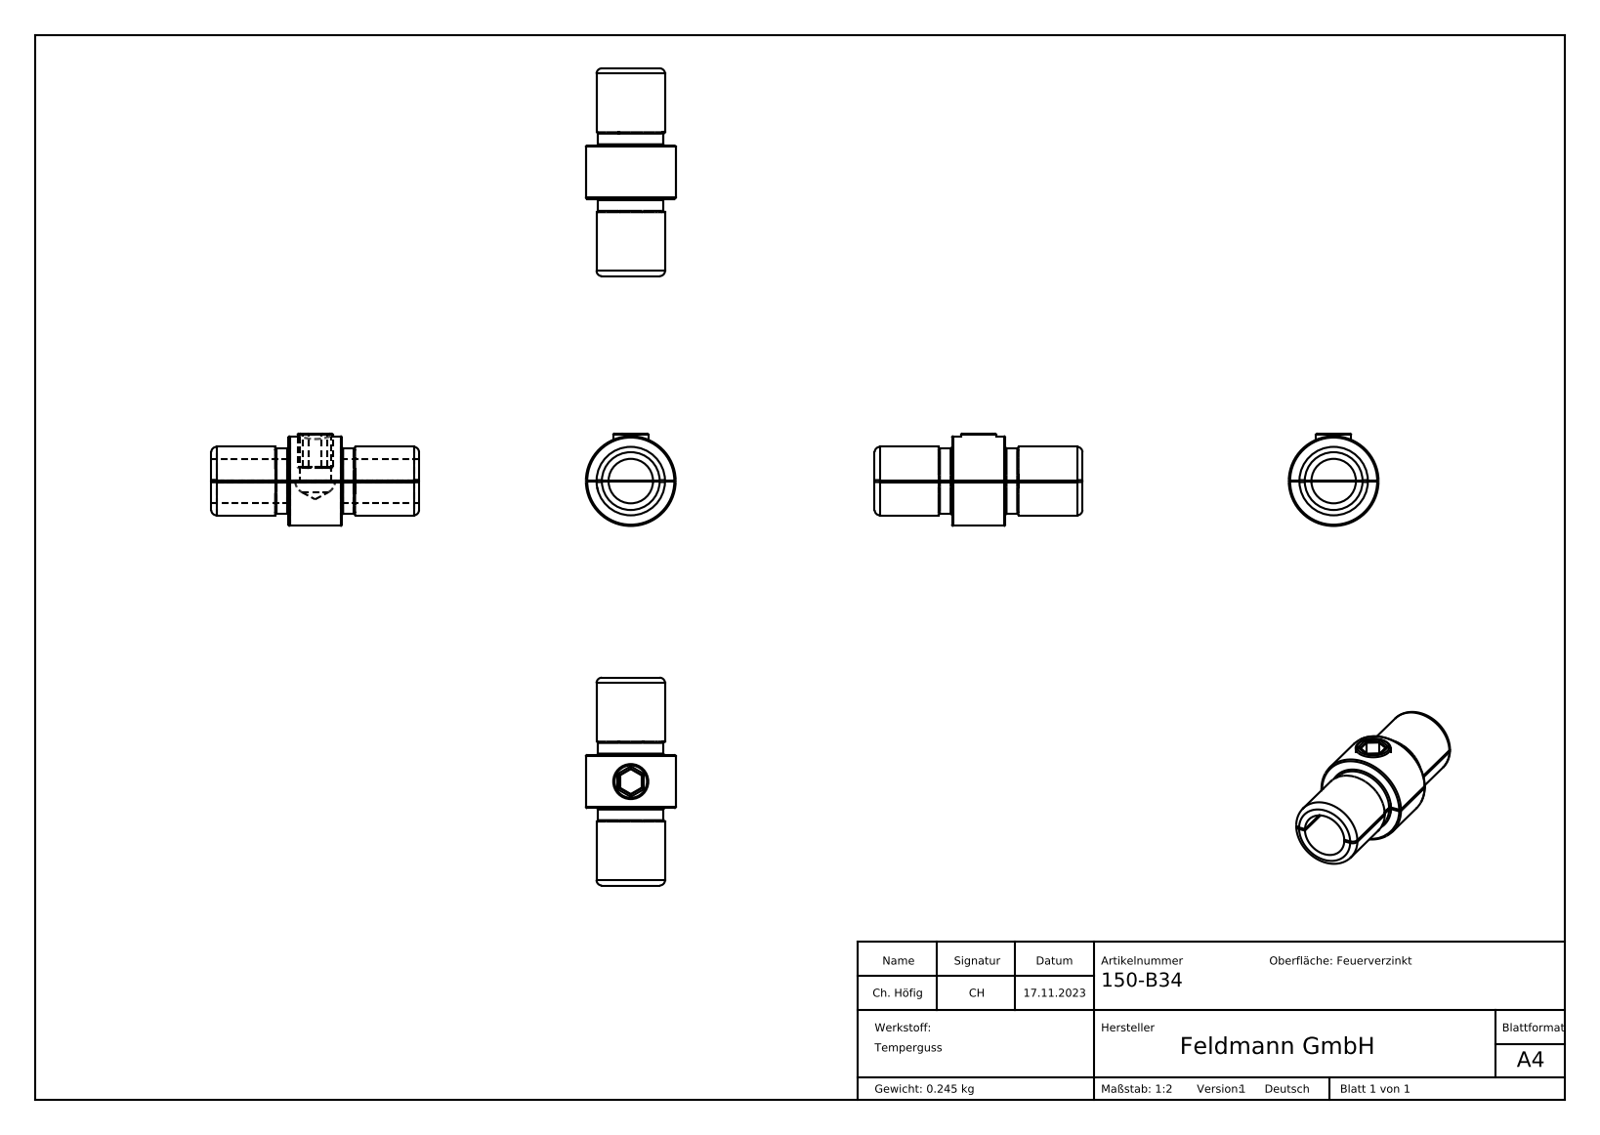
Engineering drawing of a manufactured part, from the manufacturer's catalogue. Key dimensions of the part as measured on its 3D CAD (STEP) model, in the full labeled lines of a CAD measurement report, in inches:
Part name (STEP PRODUCT): 150-B34 Teil2_150-B34 Teil2; 150-B34 Teil3_150-B34 Teil3; 150-B34; 150-B34 Teil1_150-B34 Teil1
STEP written by: SolidWorks 2018 (CONFIG_CONTROL_DESIGN)
Units: inches
Bodies: 3 solids, 219 faces (46 planar, 87 cylindrical, 86 other)
Overall size (bounding box): 3.071 × 1.366 × 1.326
Volume: 2.044 in³ · Surface area: 23.82 in²
Round holes (diameter × count): ⌀0.465 ×1, ⌀0.591 ×1, ⌀0.657 ×1
Round bosses / shafts (diameter × count): ⌀1.327 ×1, ⌀1.012 ×1, ⌀0.518 ×1
Partial cylindrical surfaces — rounded edges, fillets, slot ends (radius × count): R0.02 ×28, R0.039 ×12
Main face-to-face distances: 0.787, 1.142, 1.929, 0.319, 3.071, 0.197, 0.709, 0.697, 0.185, 0.512
